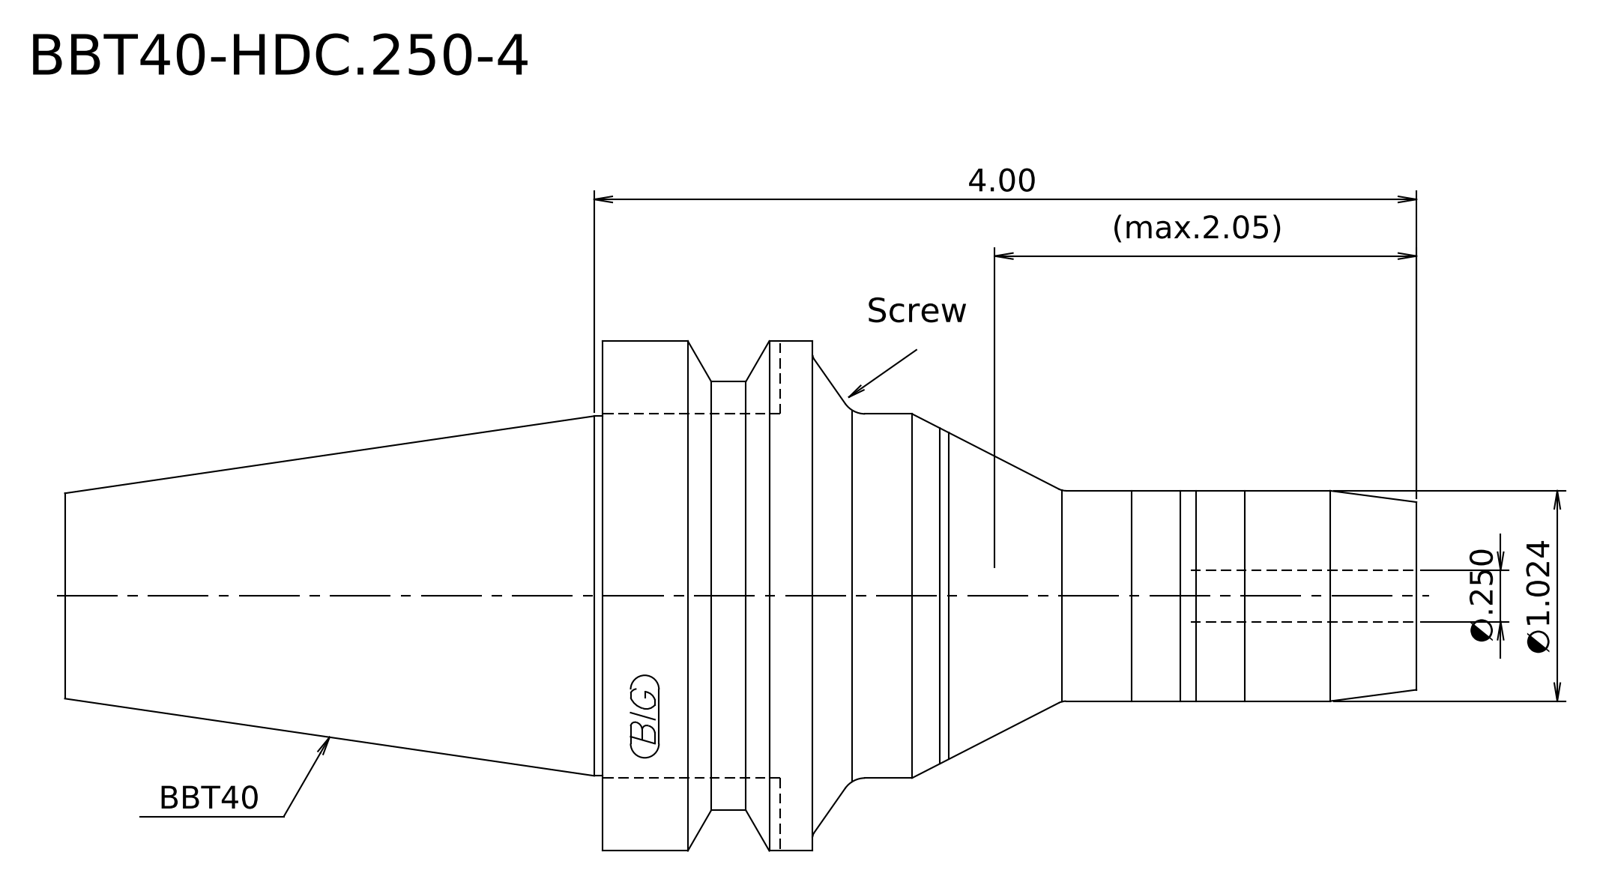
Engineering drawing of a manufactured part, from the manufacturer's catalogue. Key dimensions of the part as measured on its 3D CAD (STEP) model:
STEP written by: Kubotek KeyCreator 2011 V10.0.2 (22737) (automotive_design)
Units: millimetres
Bodies: 1 solid, 16 faces (4 planar, 6 cylindrical, 6 other)
Overall size (bounding box): 167 × 63 × 63
Volume: 204 785 mm³ · Surface area: 24 467 mm²
Round bosses / shafts (diameter × count): ⌀63 ×1, ⌀53 ×1, ⌀45 ×1, ⌀44.45 ×1, ⌀26 ×1
Main face-to-face distances: 66.4, 100.6, 167, 74.6, 26, 92.4
